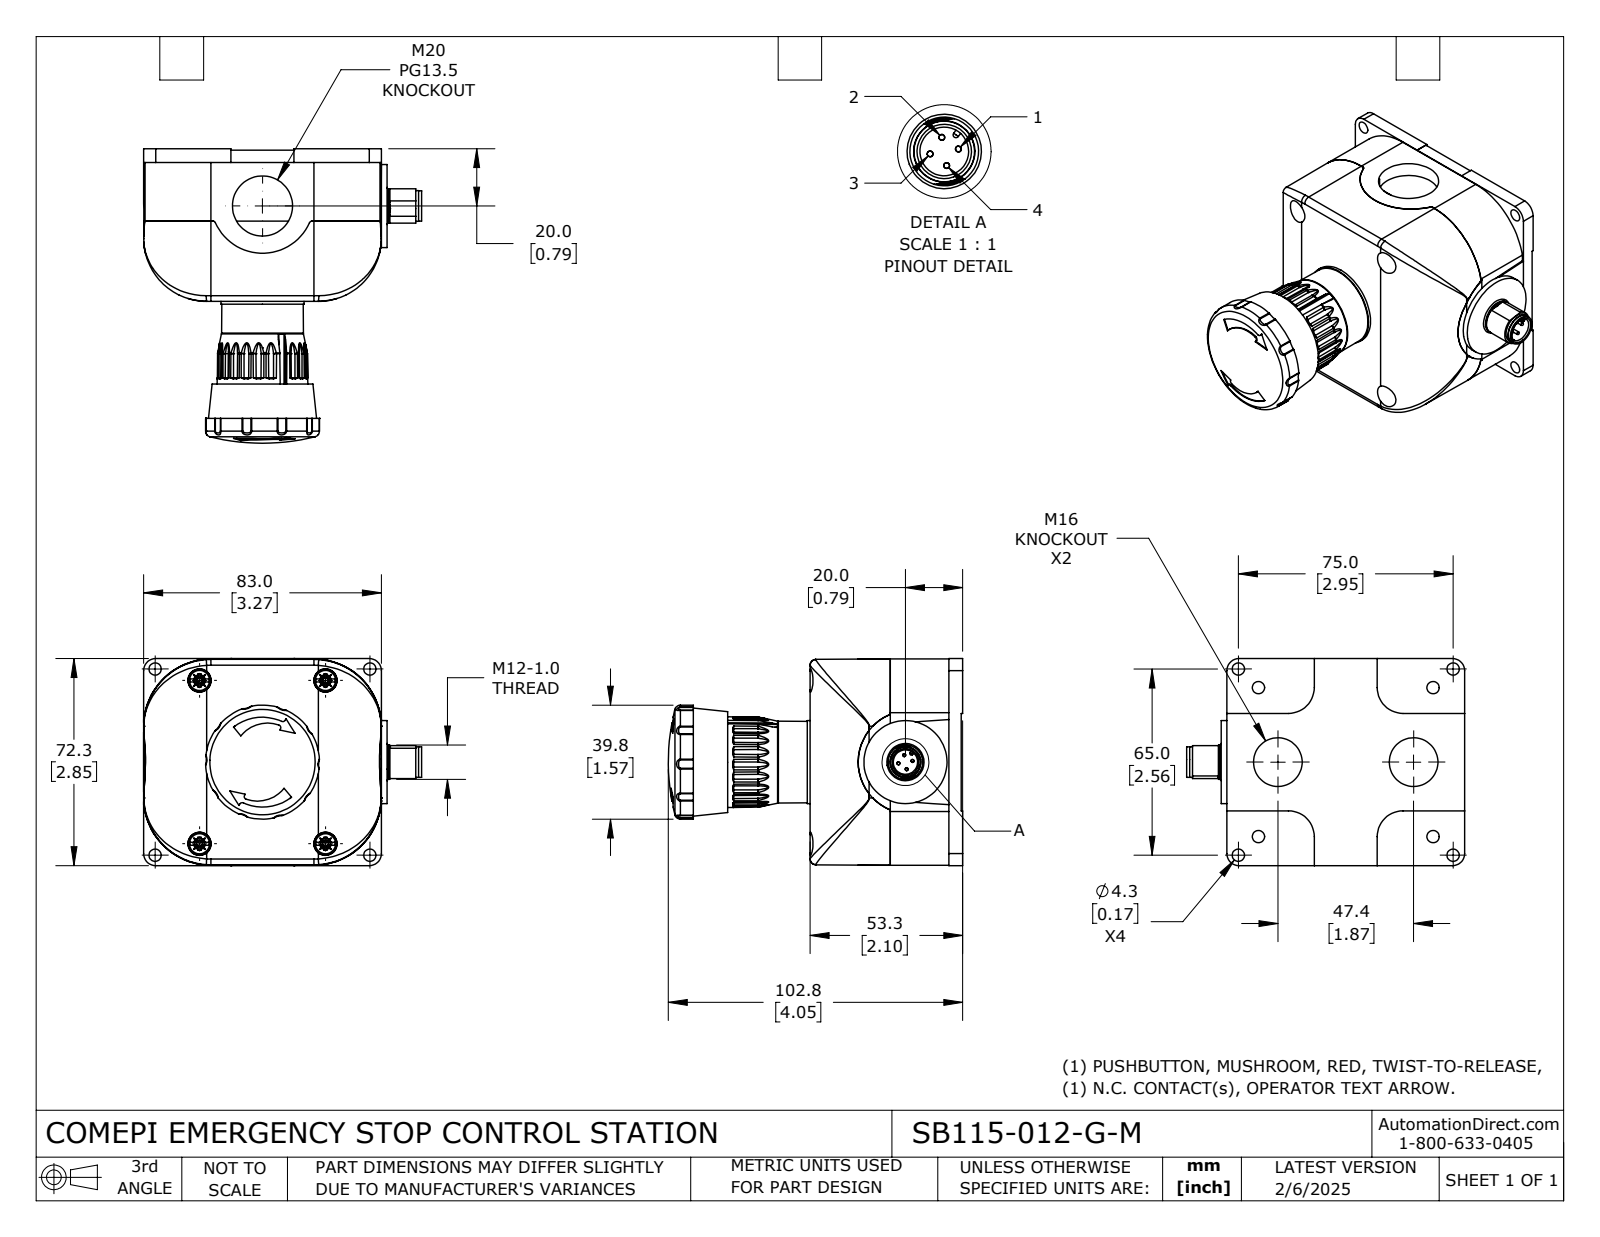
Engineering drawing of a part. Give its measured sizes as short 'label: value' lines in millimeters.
name: SB115-012-G-M
written by: SolidWorks 2024 (CONFIG_CONTROL_DESIGN)
unit: mm
bodies: 6 solids, 1119 faces (414 planar, 311 cylindrical, 394 other)
size: 102.8 × 97.1 × 72.3
volume: 241 500 mm³; area: 72 450 mm²
holes: 8× ⌀4.3, 4× ⌀1, 4× ⌀1, 4× ⌀1.7, 4× ⌀2.2, 4× ⌀8.2, 2× ⌀17, 2× ⌀21, 1× ⌀1.3, 1× ⌀8.5, 1× ⌀18.1, 1× ⌀21.7
bosses: 4× ⌀7, 4× ⌀2.2, 4× ⌀1.7, 2× ⌀29, 2× ⌀0.6, 1× ⌀26.4, 1× ⌀25, 1× ⌀24.6
rounds: 28× R1, 10× R6.8, 5× R0.5, 4× R0.9, 4× R2, 4× R9, 4× R9.7, 4× R23.5
face distances: 24.8, 2.5, 22.3, 52.8, 50.3, 28, 3, 0.5, 25.3, 53.3
hole spacings: 9.6, 26.9, 35.3, 40.1, 49.6, 58.9, 60.1, 68.3
